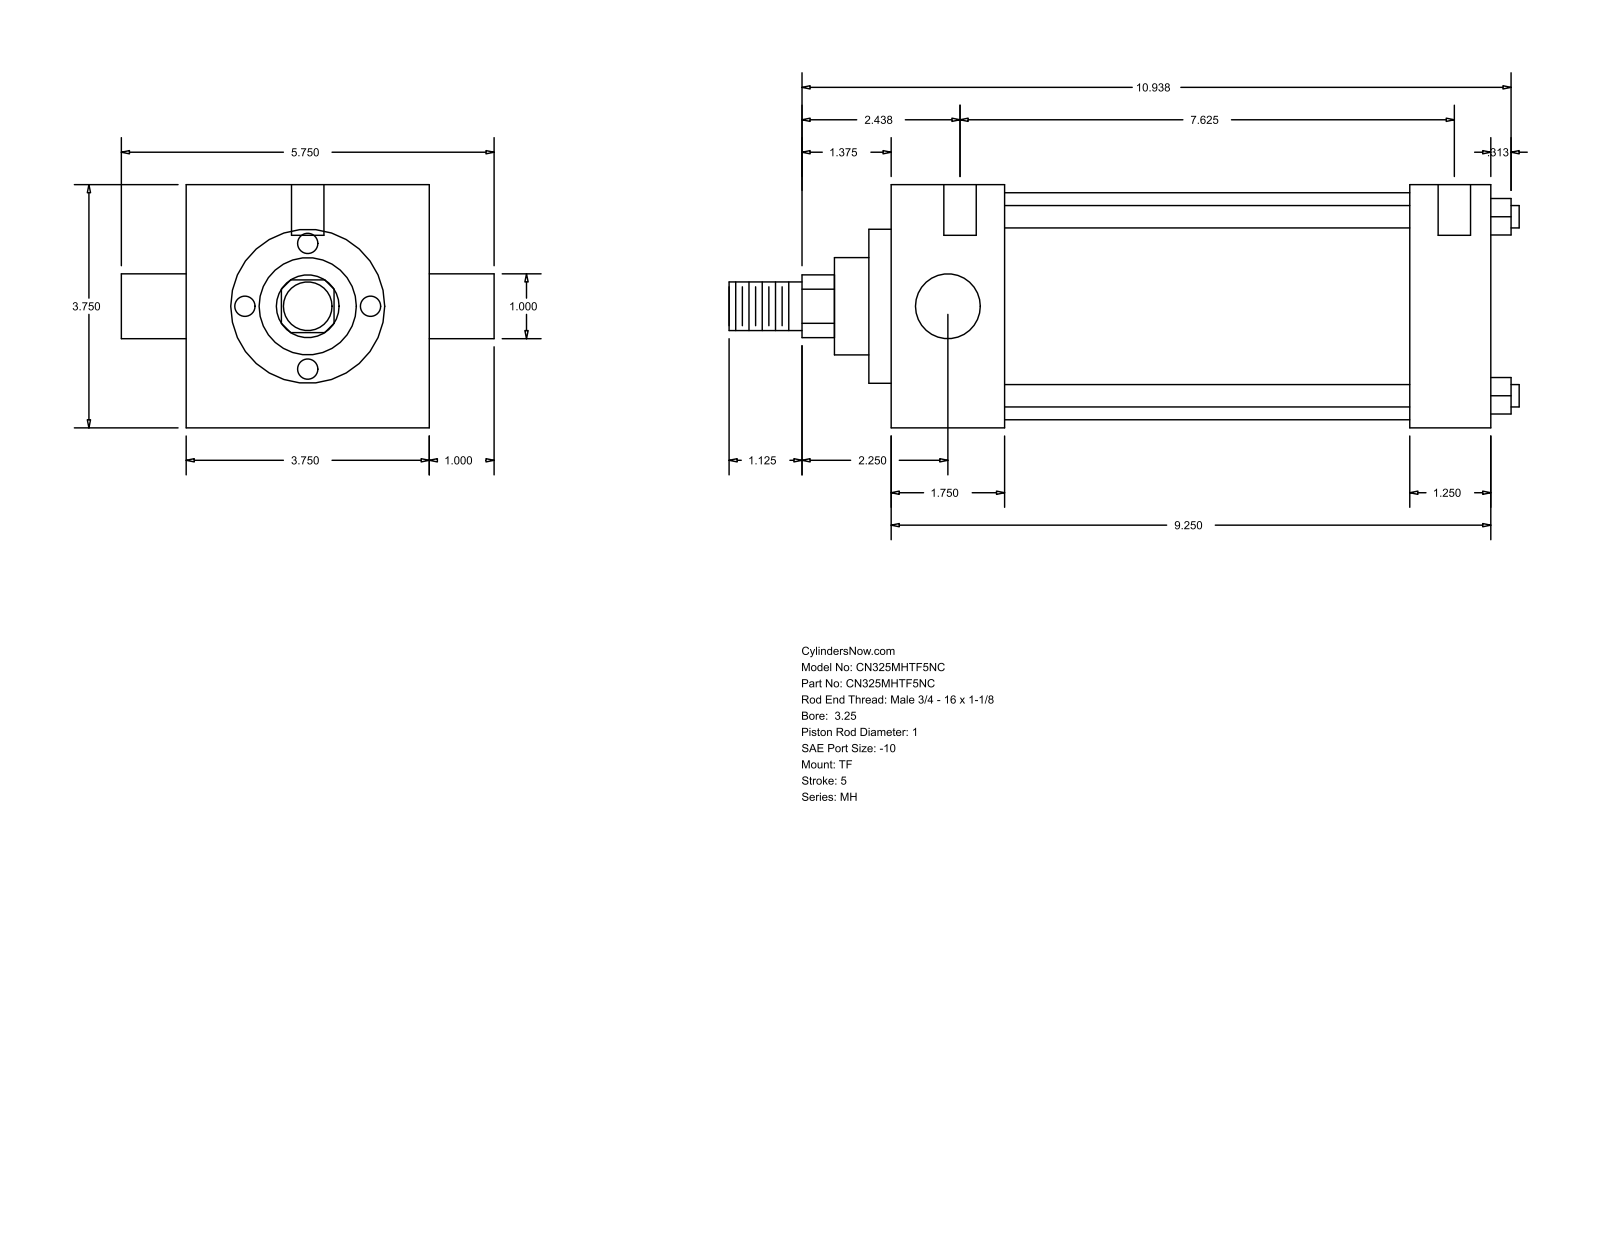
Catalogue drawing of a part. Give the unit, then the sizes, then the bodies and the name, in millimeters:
Units: millimetres
Overall size (bounding box): 309.56 × 146.05 × 95.25
Round holes (diameter × count): ⌀5.56 ×3, ⌀12.7 ×2
Round bosses / shafts (diameter × count): ⌀8.76 ×4, ⌀25.4 ×2, ⌀88.9 ×1, ⌀60.33 ×1, ⌀38.1 ×1, ⌀19.05 ×1
Partial cylindrical surfaces — rounded edges, fillets, slot ends (radius × count): R12.29 ×1
Main face-to-face distances: 95.24, 234.96, 44.46, 203.2, 158.74, 190.5, 31.76, 8.73, 53.19, 211.93
Hole centre spacings: 1.58, 4.76, 193.68, 195.26, 198.44, 200.02
Bodies: 0 solids, 86 faces (61 planar, 25 cylindrical, 0 other)
Part name (STEP PRODUCT): MH_TF__0325_1
STEP written by: GSSL Pune (CONFIG_CONTROL_DESIGN)
